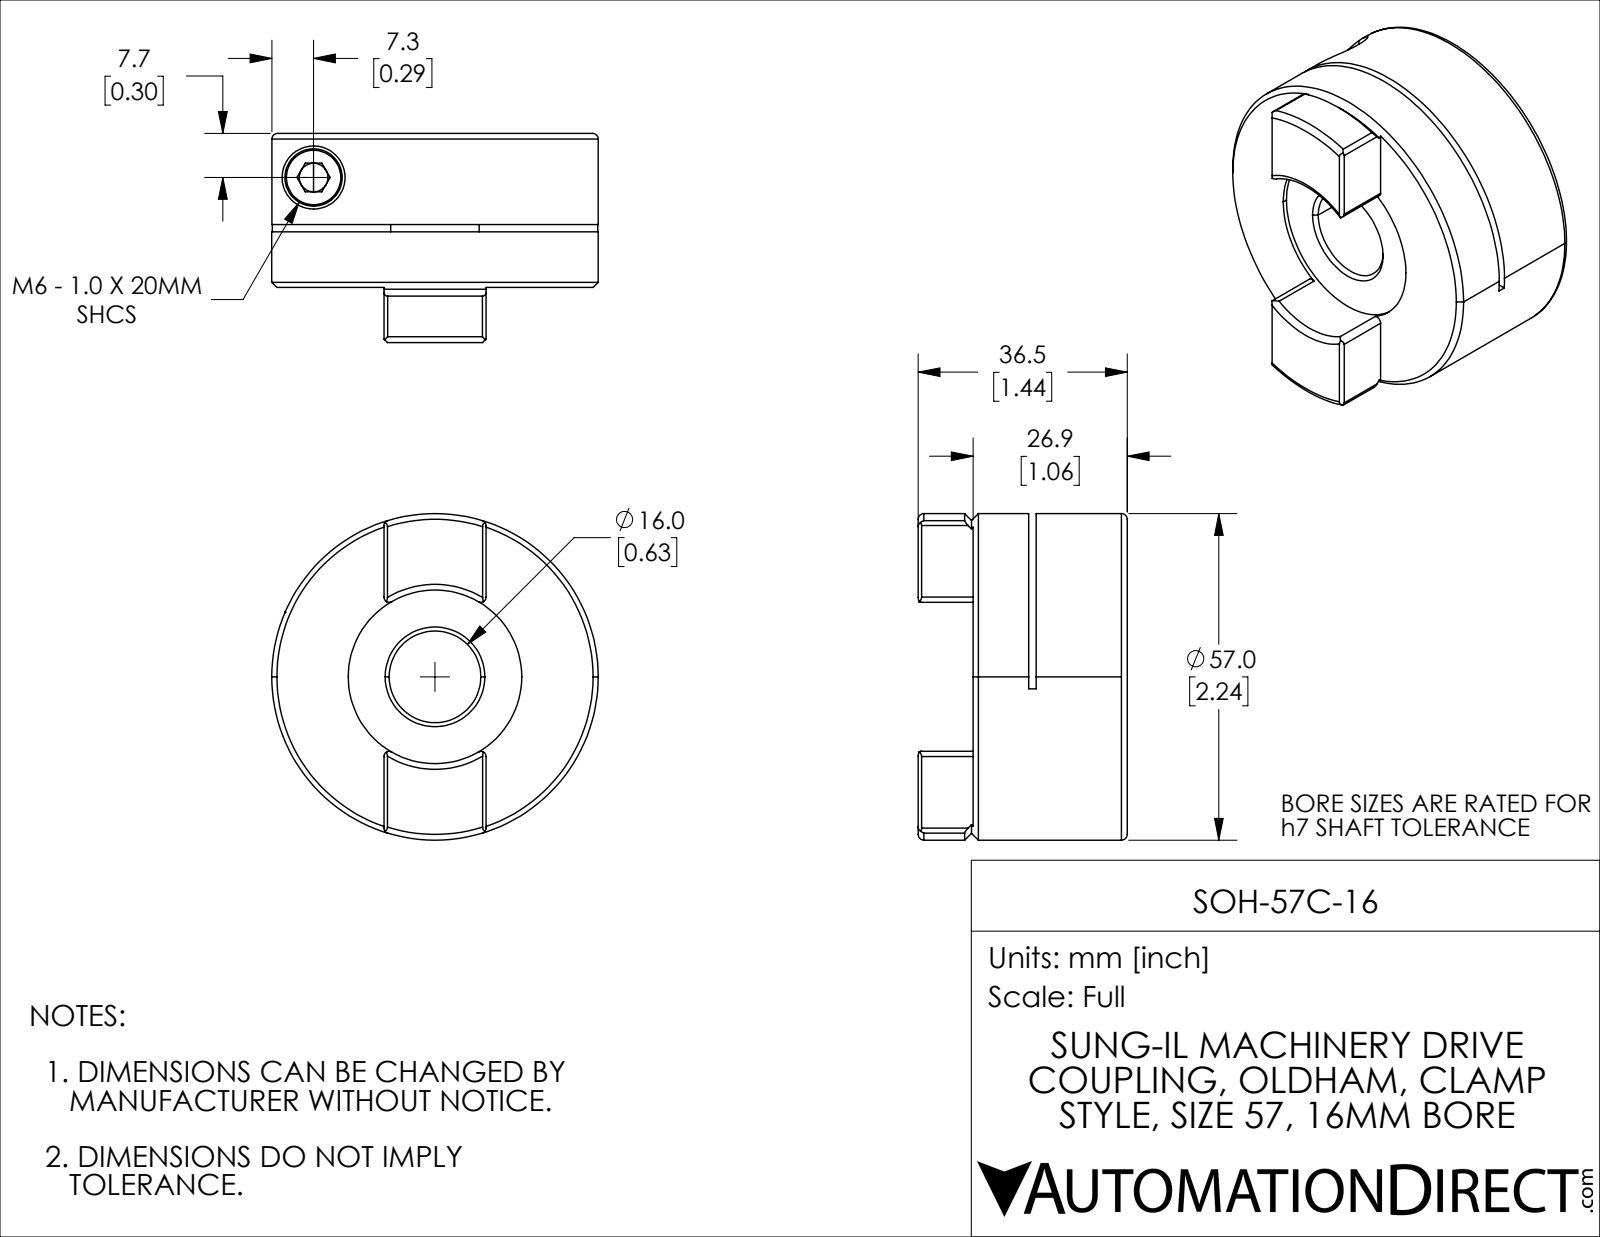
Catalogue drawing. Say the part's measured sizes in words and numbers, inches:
The part is named "SOH-57C-16". Its 3-D file was written by "SolidWorks 2021 (CONFIG_CONTROL_DESIGN)". It is 2 solids with 97 faces: 39 planar, 33 cylindrical and 25 other. Overall it measures 2.244 by 2.244 by 1.437 inches. Its volume is 3.924 cubic inches and its surface area 25.64 square inches. Round holes: 1 of diameter 0.197, 1 of diameter 0.252, 1 of diameter 0.433, 1 of diameter 0.63, 1 of diameter 1.193. Round bosses or shafts: 1 of diameter 2.244, 1 of diameter 0.394, 1 of diameter 0.236. Partial cylindrical surfaces (rounded edges, fillets, slot ends): 8 of radius 0.035, 1 of radius 1.575. The main face-to-face distances are 0.051, 0.677, 0.626, 1.059, 0.433, 0.382, 0.402, 1.028, 0.35, 0.031.
